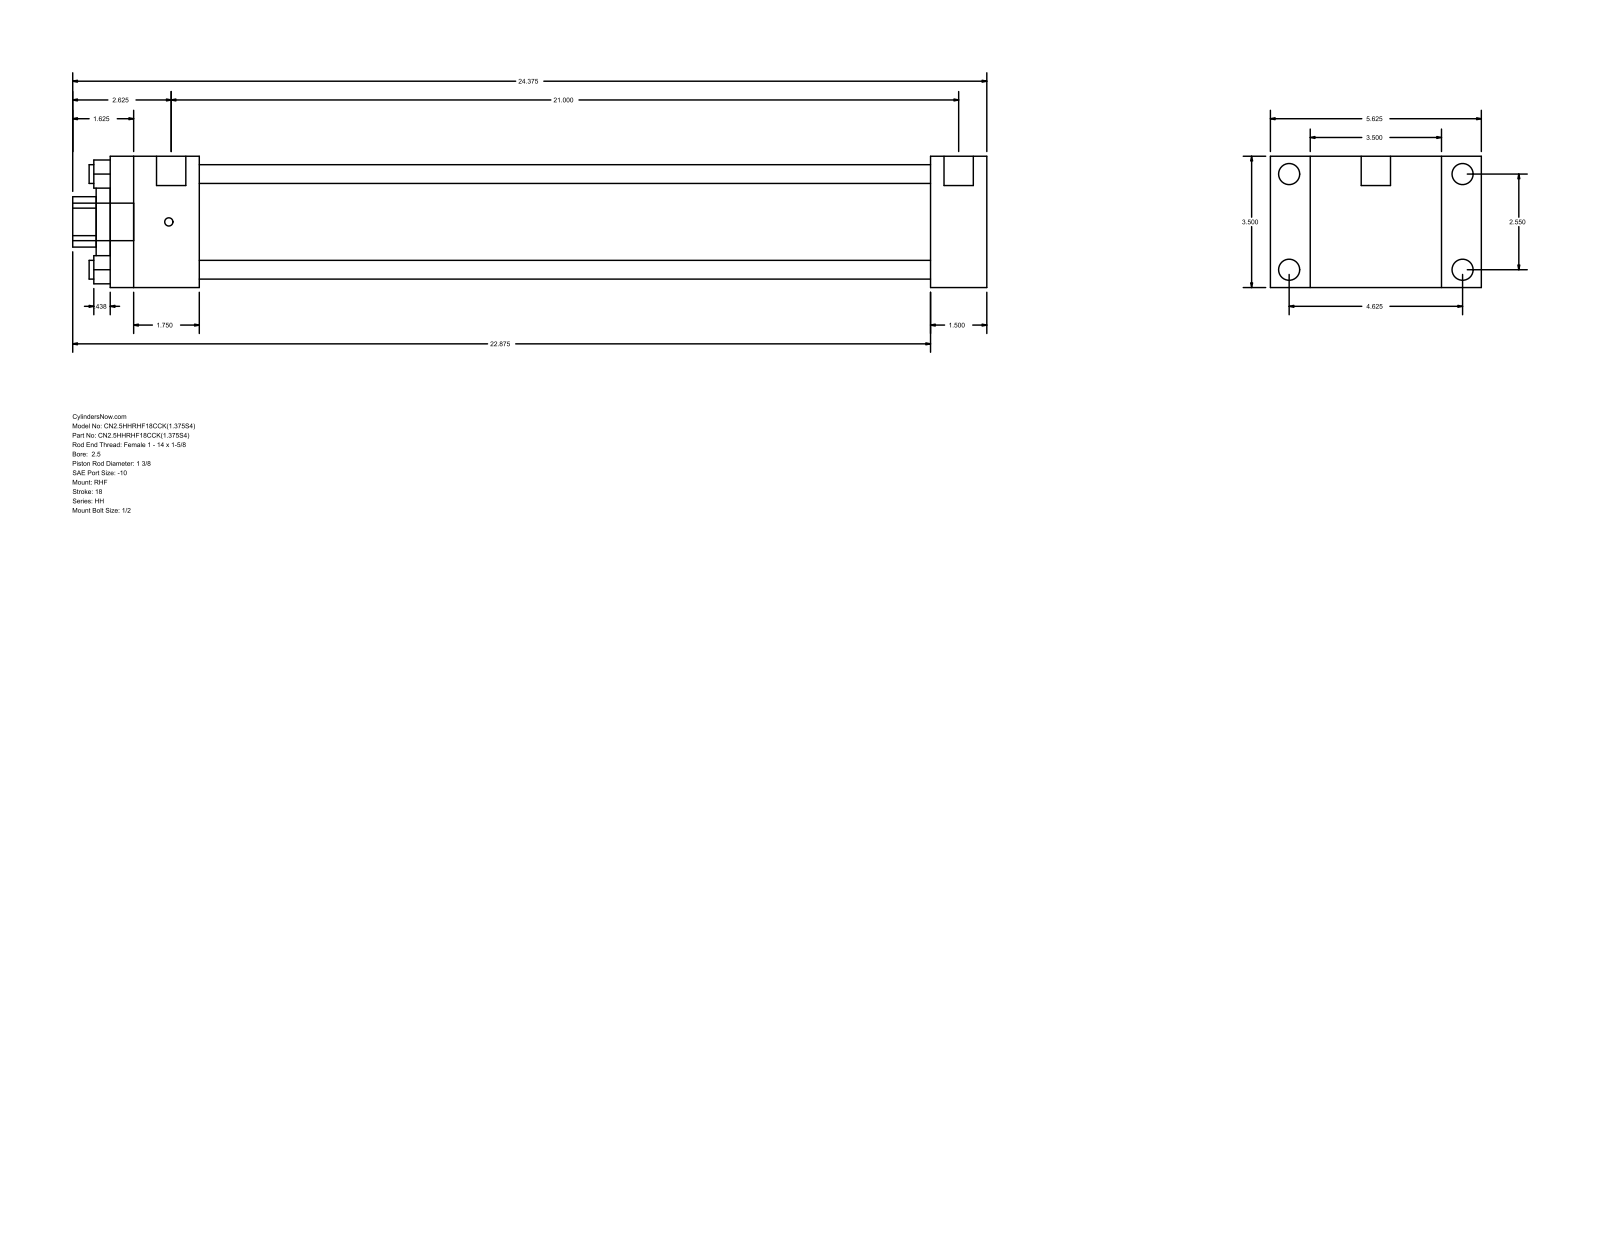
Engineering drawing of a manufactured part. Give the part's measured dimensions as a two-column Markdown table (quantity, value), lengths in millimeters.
| quantity | value |
| --- | --- |
| part name | HH_RHF__0250_1.375 |
| STEP written by | GSSL Pune (CONFIG_CONTROL_DESIGN) |
| units | millimeters |
| bodies | 0 solids, 88 faces (60 planar, 28 cylindrical, 0 other) |
| overall size | 619.12 × 142.88 × 88.9 |
| round holes (diameter × count) | 12.7 × 4, 34.92 × 1, 50.8 × 1, 73.03 × 1 |
| round bosses / shafts (diameter × count) | 14.3 × 4, 5.56 × 4, 19.84 × 2, 25.4 × 1 |
| partial cylindrical surfaces (radius × count) | 17.06 × 1 |
| main face-to-face distances | 88.9, 38.1, 26.99, 115.89, 555.62, 593.72, 142.88, 60.32, 495.3, 533.4 |
| hole center spacings | 45.79, 64.76, 91.58 |
